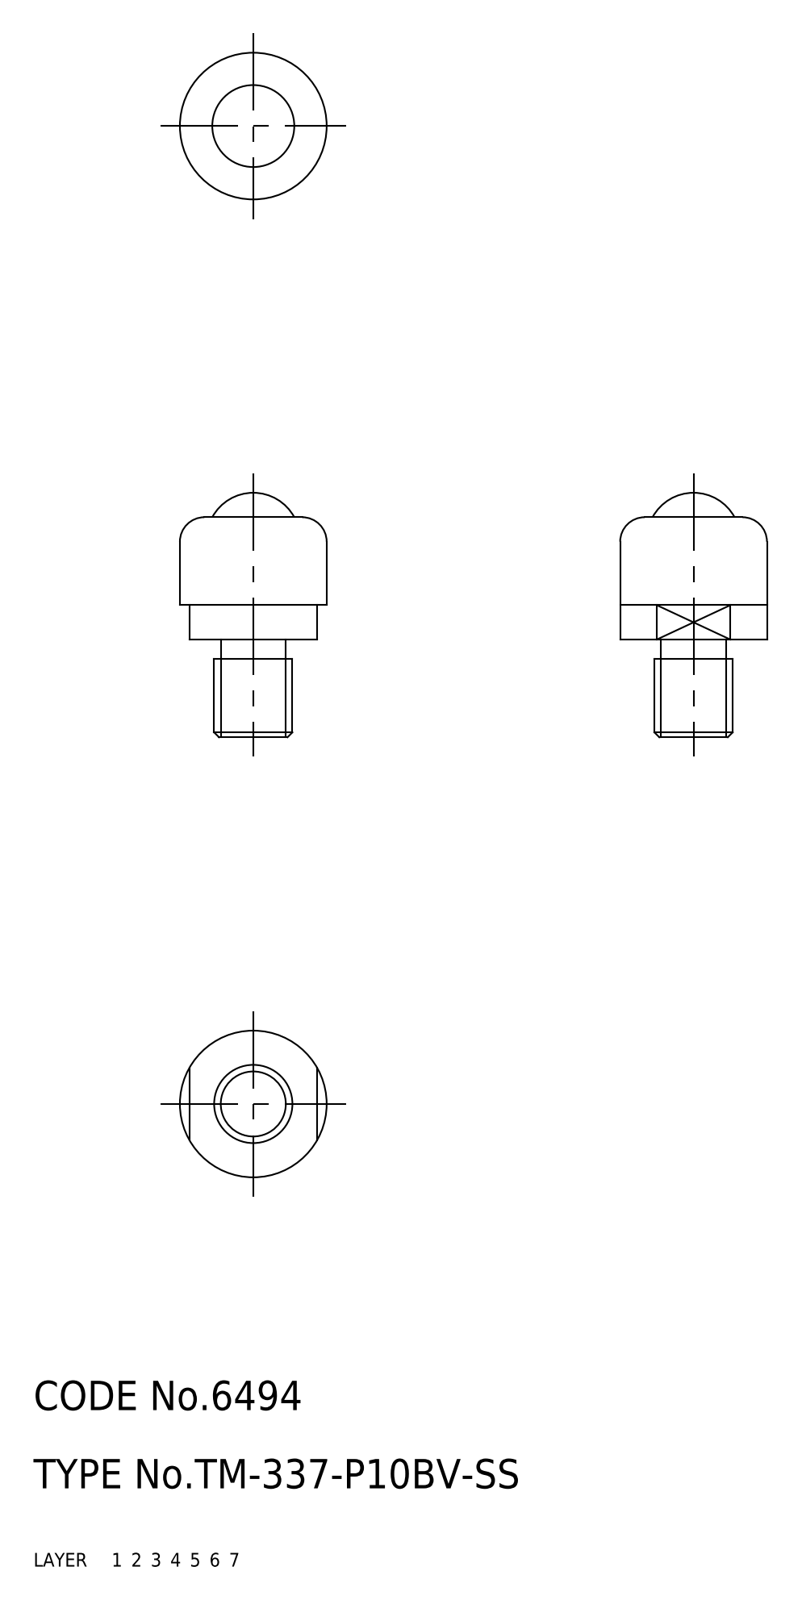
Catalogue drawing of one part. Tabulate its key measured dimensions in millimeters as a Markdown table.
| quantity | value |
| --- | --- |
| part name | pan; TM_337_P10BV_SS; ball_A; housing |
| STEP written by | SolidWorks 2015 (AUTOMOTIVE_DESIGN) |
| units | millimeters |
| bodies | 3 solids, 29 faces (9 planar, 12 cylindrical, 8 other) |
| overall size | 25 × 15 × 15 |
| volume | 1 814 mm³ |
| surface area | 1 984 mm² |
| round holes (diameter × count) | 9 × 1, 13.6 × 1 |
| round bosses / shafts (diameter × count) | 15 × 1, 8 × 1, 6.65 × 1 |
| main face-to-face distances | 3.5, 10, 13.5, 13, 8, 2, 5.5, 21.8, 13.8, 11.8 |
